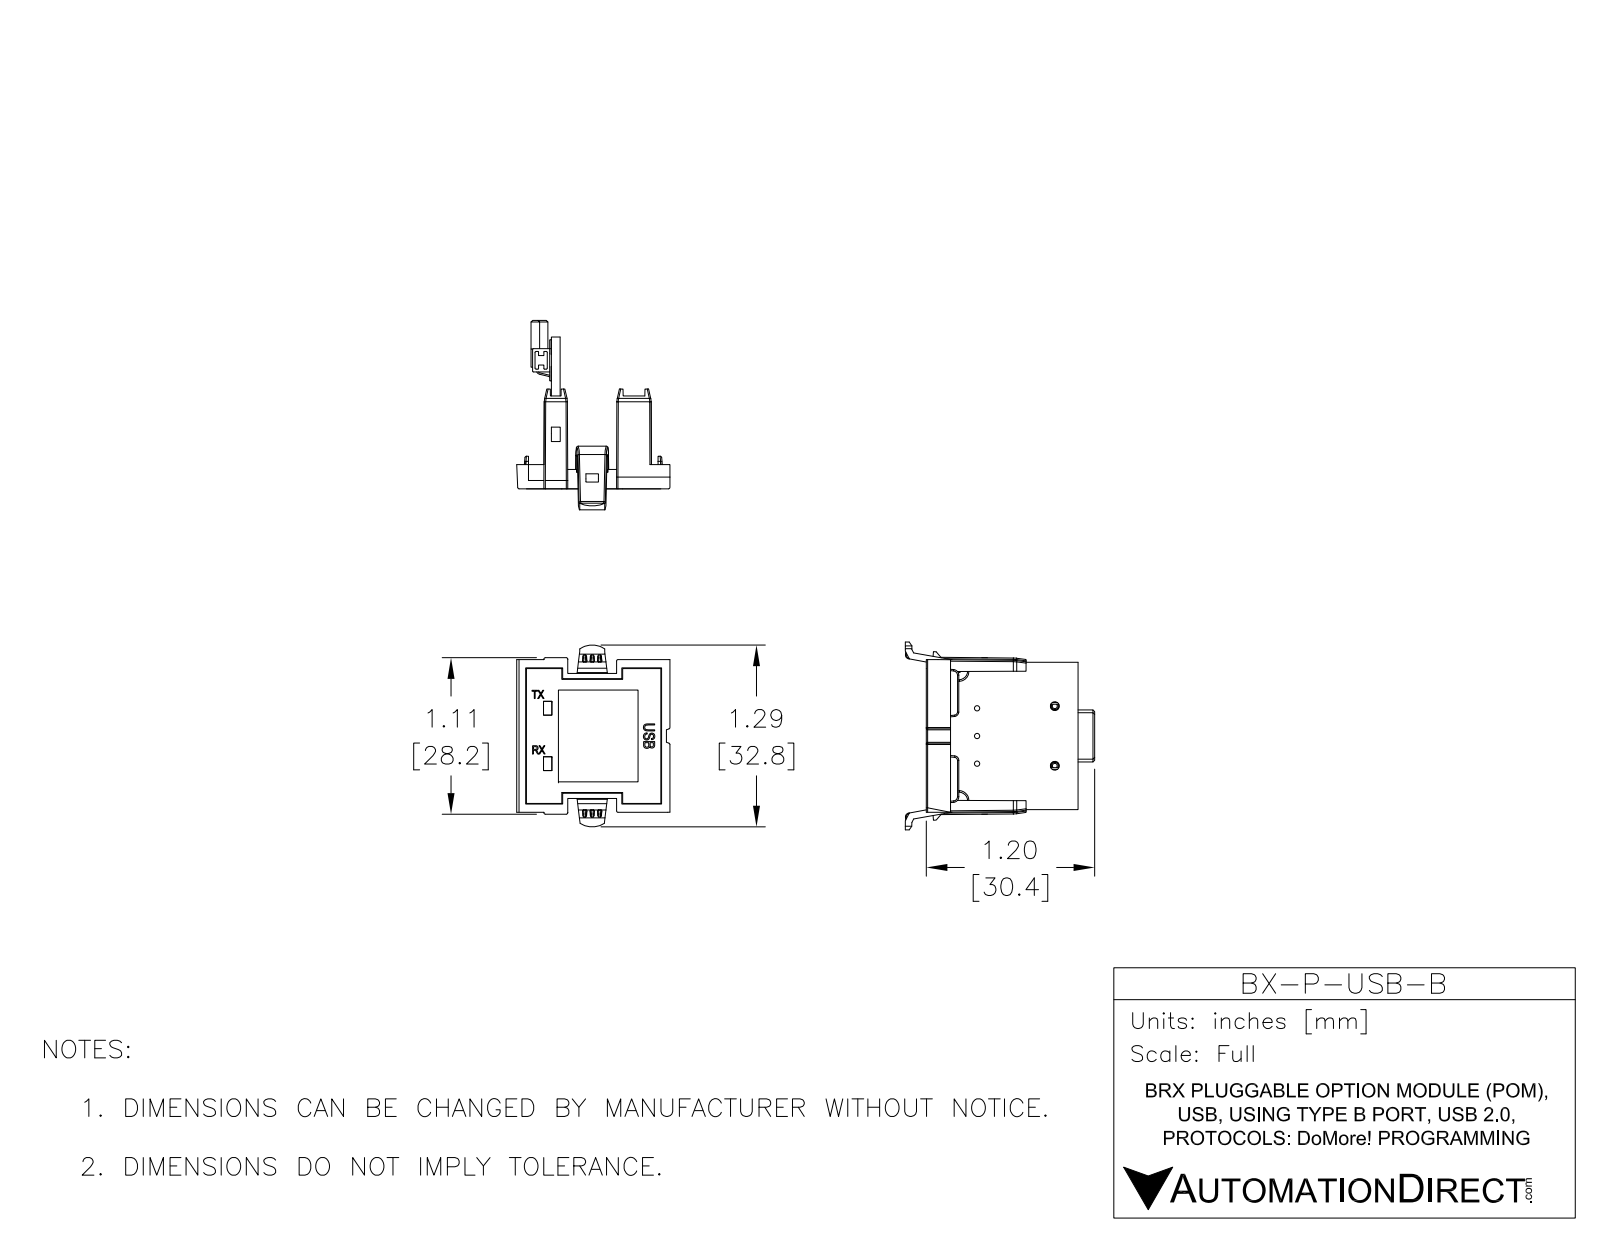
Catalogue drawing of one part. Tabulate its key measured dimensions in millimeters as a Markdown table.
| quantity | value |
| --- | --- |
| part name | BX-P-USB-B |
| STEP written by | SolidWorks 2016 (AUTOMOTIVE_DESIGN) |
| units | millimeters |
| bodies | 43 solids, 1741 faces (1436 planar, 236 cylindrical, 69 other) |
| overall size | 33.9 × 33.88 × 27.53 |
| volume | 4 839 mm³ |
| surface area | 8 344 mm² |
| round holes (diameter × count) | 0.95 × 3, 1.6 × 2 |
| partial cylindrical surfaces (radius × count) | 0.2 × 47, 0.1 × 40, 0.85 × 10, 0.14 × 8, 0.41 × 5, 1.25 × 5, 0.25 × 4, 2.75 × 4 |
| main face-to-face distances | 1.58, 1.57, 1.68, 1.67, 0.5, 1.4, 11.18, 2.97, 12.85, 12.75 |
| hole center spacings | 14.03, 4.99, 5, 9.99, 10.77, 15.02, 15.03, 17.44 |
